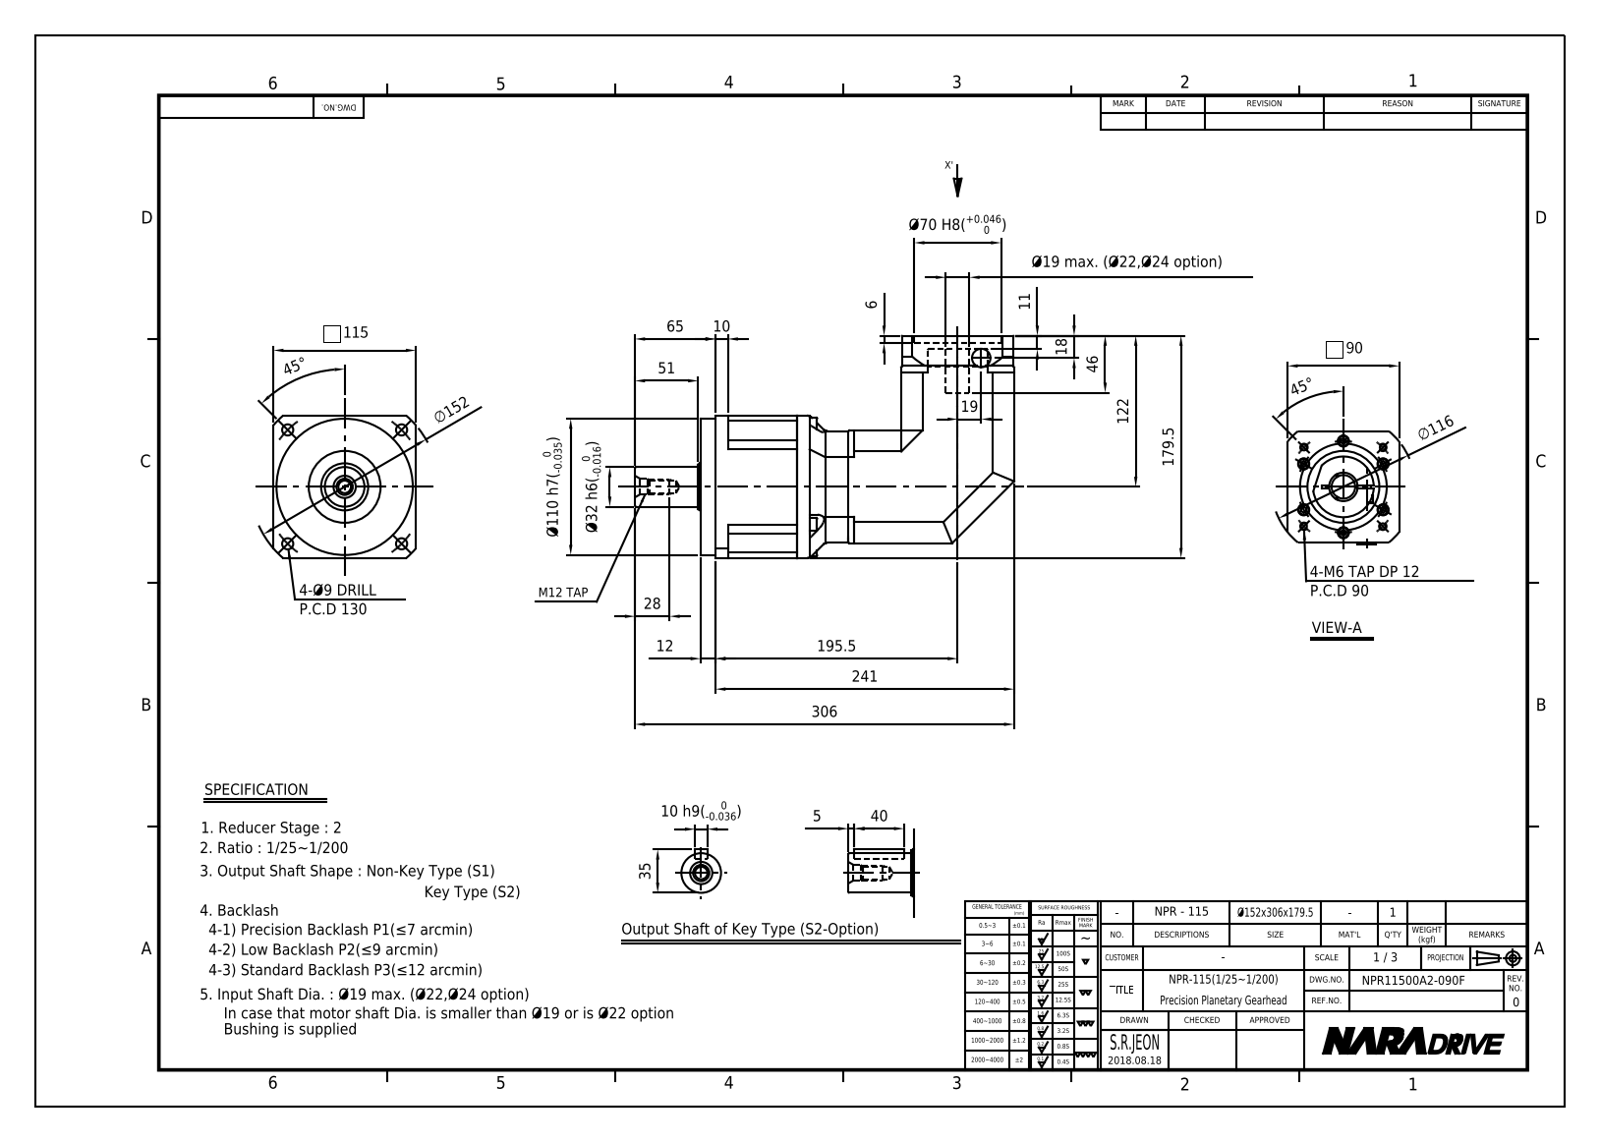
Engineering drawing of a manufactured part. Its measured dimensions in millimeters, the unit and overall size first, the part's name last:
Units: millimetres
Overall size (bounding box): 306 × 179.5 × 115
Round holes (diameter × count): ⌀9 ×14, ⌀4.13 ×10, ⌀5.5 ×10, ⌀4.92 ×9, ⌀6.6 ×5, ⌀58 ×2, ⌀7 ×1, ⌀8.5 ×1, ⌀10.11 ×1, ⌀10.25 ×1, ⌀19 ×1, ⌀23 ×1
Round bosses / shafts (diameter × count): ⌀8.5 ×10, ⌀5 ×10, ⌀10 ×5, ⌀6 ×5, ⌀110 ×1, ⌀49 ×1, ⌀38 ×1, ⌀32 ×1
Partial cylindrical surfaces — rounded edges, fillets, slot ends (radius × count): R0.5 ×8, R5 ×8, R12.5 ×8, R51.5 ×2, R5.5 ×1, R35 ×1, R51 ×1, R58 ×1
Main face-to-face distances: 12, 103, 91, 10, 68, 0.5, 90.5, 115, 12.5, 102.5
Hole centre spacings: 37, 23.82, 74.31, 45.92, 12.5, 13.32, 17.38, 32.24
Volume: 2 182 000 mm³ · Surface area: 231 394 mm²
Bodies: 2 solids, 588 faces (293 planar, 155 cylindrical, 140 other)
Part name (STEP PRODUCT): NPR11500A2-090F-S1
STEP written by: Autodesk Inventor 2015 (AUTOMOTIVE_DESIGN)
